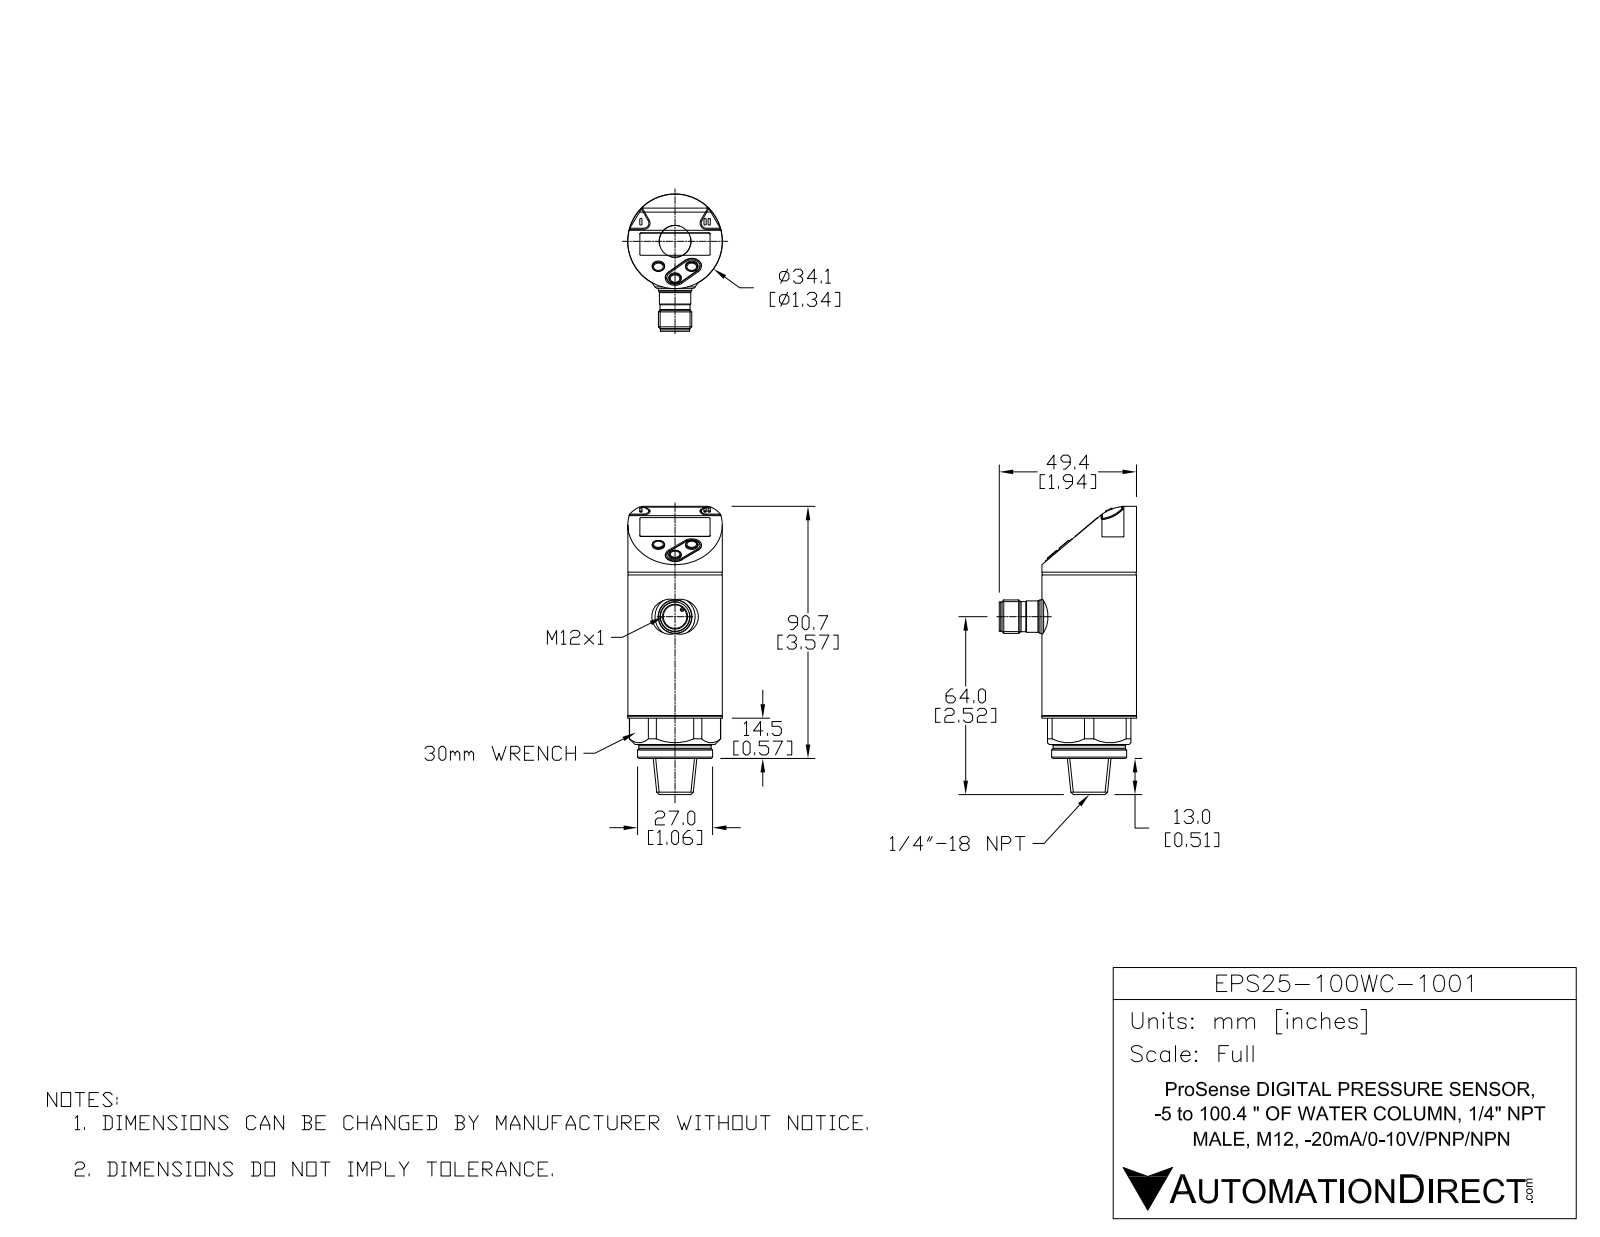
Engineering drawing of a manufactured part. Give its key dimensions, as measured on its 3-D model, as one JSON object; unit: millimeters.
{"part_name": "EPS25-100WC-1001", "step_written_by": "SolidWorks 2016 (AUTOMOTIVE_DESIGN)", "units": "millimeters", "bodies": {"solids": 11, "faces": 370, "planar": 207, "cylindrical": 84, "other": 79}, "overall_size": [103.7, 49.4, 34.1], "volume_mm3": 72203, "surface_area_mm2": 21365, "round_holes": [[4.2, 1], [8.45, 1]], "round_bosses_or_shafts": [[1.4, 4], [1, 4], [34.1, 1], [34, 1], [33.8, 1], [27, 1], [26, 1], [12, 1]], "partial_cylinders_radius": [[1.8, 2], [2.2, 2], [3, 2], [3.5, 2], [15, 2], [0.61, 1], [6.8, 1], [16.44, 1]], "face_to_face_distances": [0.68, 11.5, 12.18, 10.68, 1.5, 10, 2, 2.5, 14, 4]}
